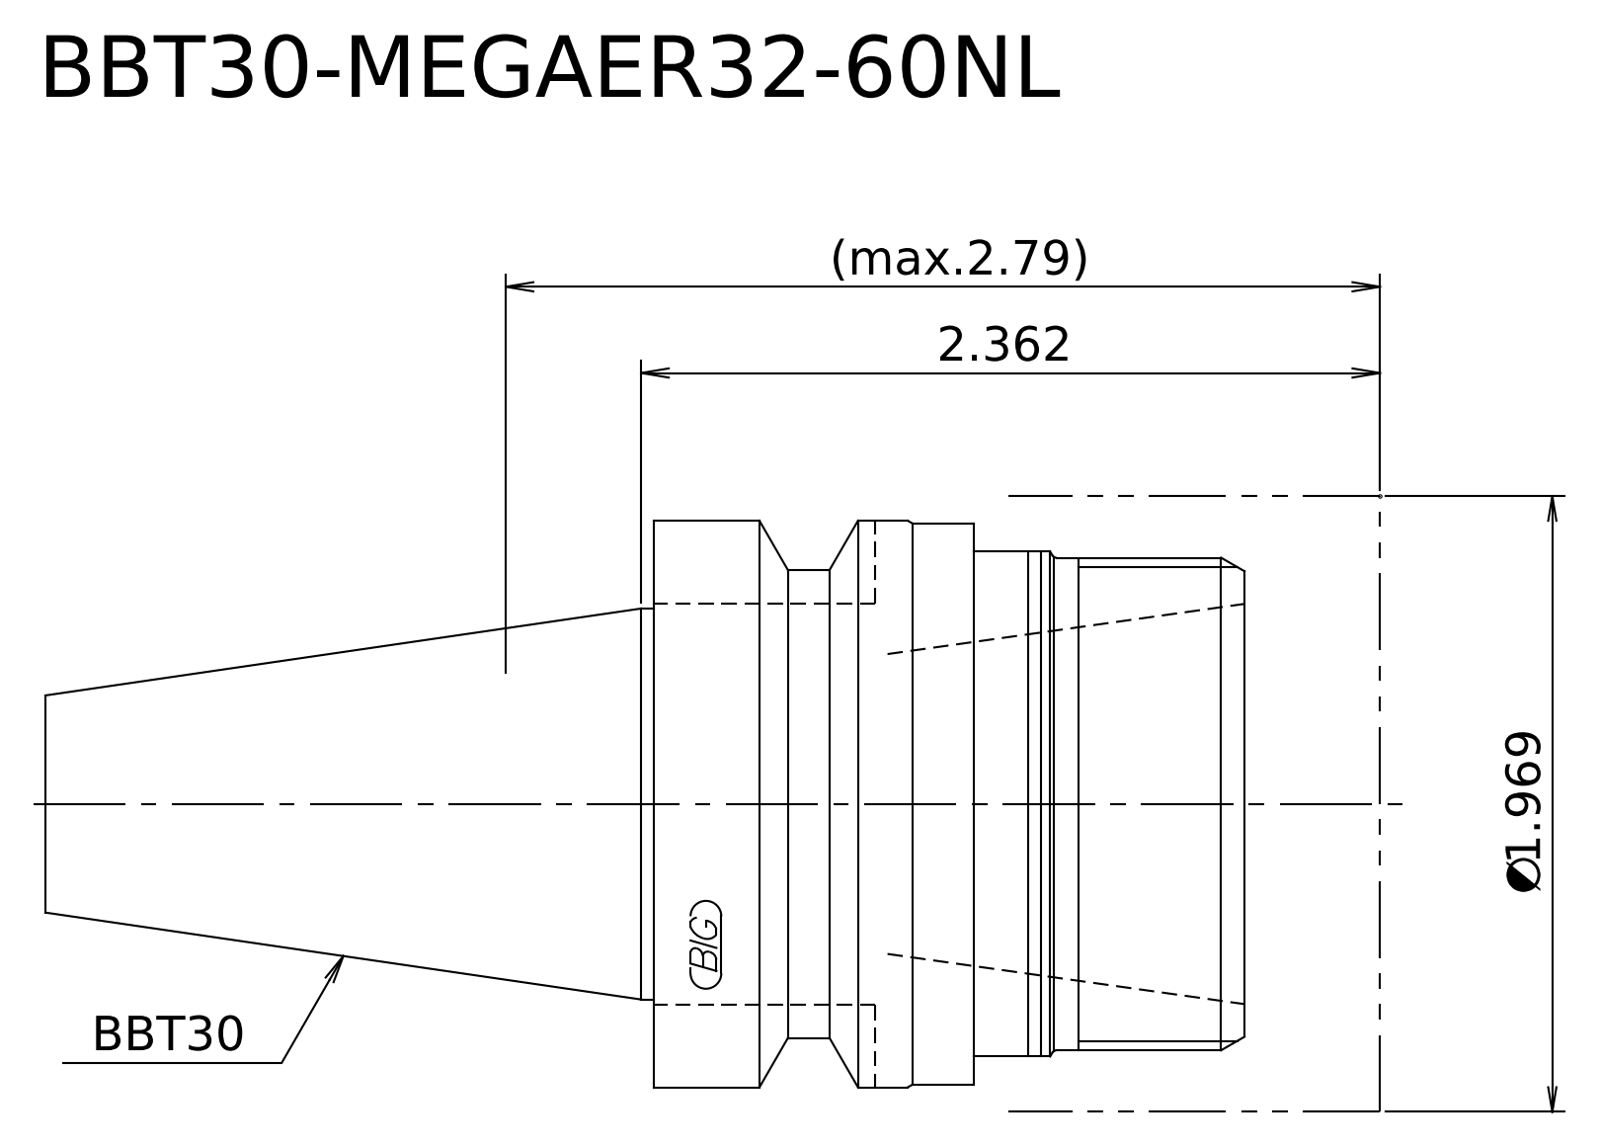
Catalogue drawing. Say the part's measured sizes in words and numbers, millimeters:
Its 3-D file was written by "Kubotek KeyCreator 2011 V10.0.2 (22737) (automotive_design)". It is 2 solids with 20 faces: 6 planar, 8 cylindrical and 6 other. Overall it measures 108.4 by 50 by 50 millimeters. Its volume is 151 836 cubic millimeters and its surface area 22 190 square millimeters. Round bosses or shafts: 1 of diameter 50, 1 of diameter 46, 1 of diameter 45.6, 1 of diameter 41, 1 of diameter 40, 1 of diameter 38, 1 of diameter 31.75. The main face-to-face distances are 30.2, 11, 19.2, 59, 48, 28.8, 33, 22, 2.8, 26.
